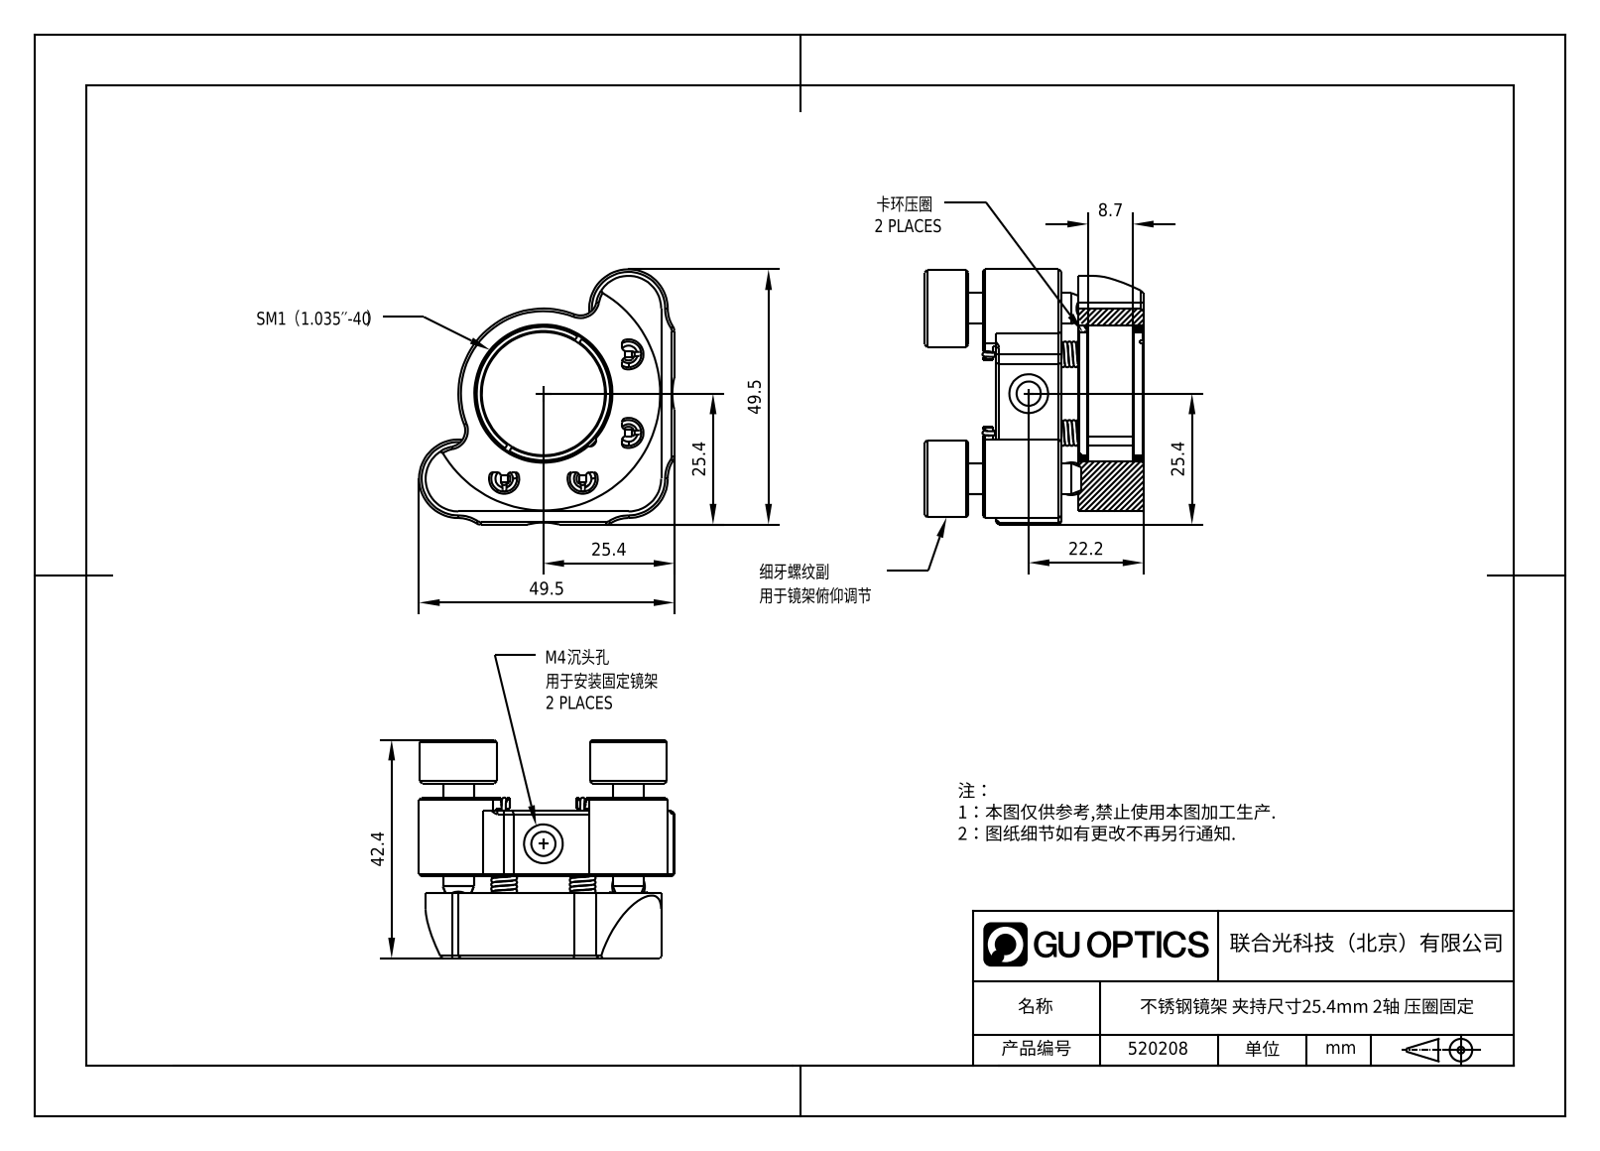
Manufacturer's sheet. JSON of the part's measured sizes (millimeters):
{"part_name": "36.1，440c不锈钢滚珠_36.1.6_GZ-B4; 36.1，440c不锈钢滚珠_36.1.35_GZ-B6.35; DXG，平面螺纹旋钮_3.2.10.19-DXG-M0625-15-8.5S; 1.1.20.13-ZJO-SM1.0-2 (+4 more)", "step_written_by": "SolidWorks 2021 (CONFIG_CONTROL_DESIGN)", "units": "millimeters", "bodies": {"solids": 21, "faces": 578, "planar": 180, "cylindrical": 161, "other": 237}, "overall_size": [49.53, 49.53, 42.41], "volume_mm3": 27111, "surface_area_mm2": 18956, "round_holes": [[6.35, 6], [2.01, 2], [3.99, 2], [4, 2], [4.7, 2], [6, 2], [7, 2], [7.54, 2], [23.89, 1]], "round_bosses_or_shafts": [[4, 6], [15.24, 2], [15, 2], [26.29, 1]], "partial_cylinders_radius": [[0.79, 16], [6.48, 14], [0.64, 8], [1, 4], [1.93, 4], [2.92, 4], [6.35, 3], [1.59, 2]], "face_to_face_distances": [12.7, 15.87, 2.54, 3.17, 15.24, 31.11, 18.41, 28.57, 13.84, 26.54], "hole_center_spacings": [18.18, 5, 8.89, 15.24, 23.35, 24.13, 25.72, 34.2]}
